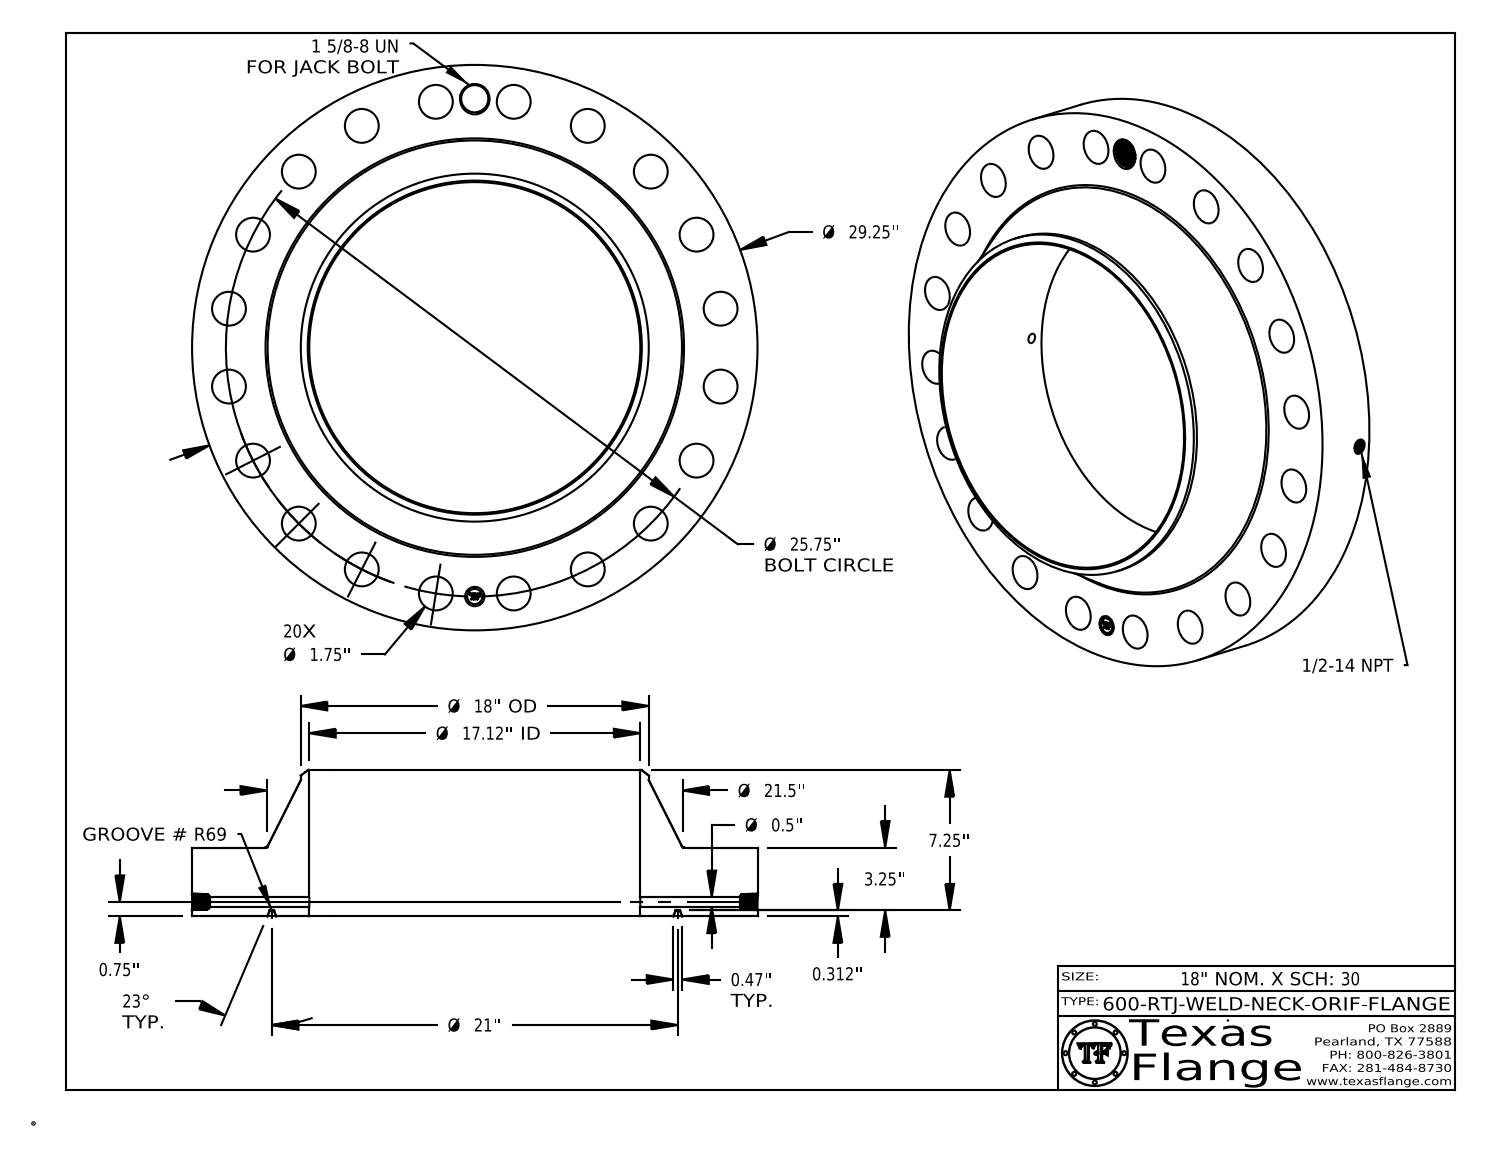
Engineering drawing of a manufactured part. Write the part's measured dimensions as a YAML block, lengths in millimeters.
part_name: "600-RTJ-WELD-NECK"
step_written_by: "CATIA V5 STEP AP214 (AUTOMOTIVE_DESIGN)"
units: millimeters
bodies: {solids: 1, faces: 881, planar: 370, cylindrical: 142, other: 369}
overall_size: [743, 743, 192.1]
volume: 27250000
surface_area: 1383000
round_holes:
  - {diameter: 44.5, count: 20}
  - {diameter: 12.7, count: 1}
  - {diameter: 17.1, count: 1}
  - {diameter: 25.4, count: 1}
  - {diameter: 35.8, count: 1}
  - {diameter: 434.9, count: 1}
round_bosses_or_shafts:
  - {diameter: 1.5, count: 8}
  - {diameter: 743, count: 1}
  - {diameter: 457.2, count: 1}
  - {diameter: 20, count: 1}
face_to_face_distances: [90.5, 7.9, 82.6, 192.1, 184.2, 101.6, 0.4, 90.1, 82.2, 102]
hole_center_spacings: [384.4, 622, 646, 327, 296.9, 102.3, 202.1, 462.5]
